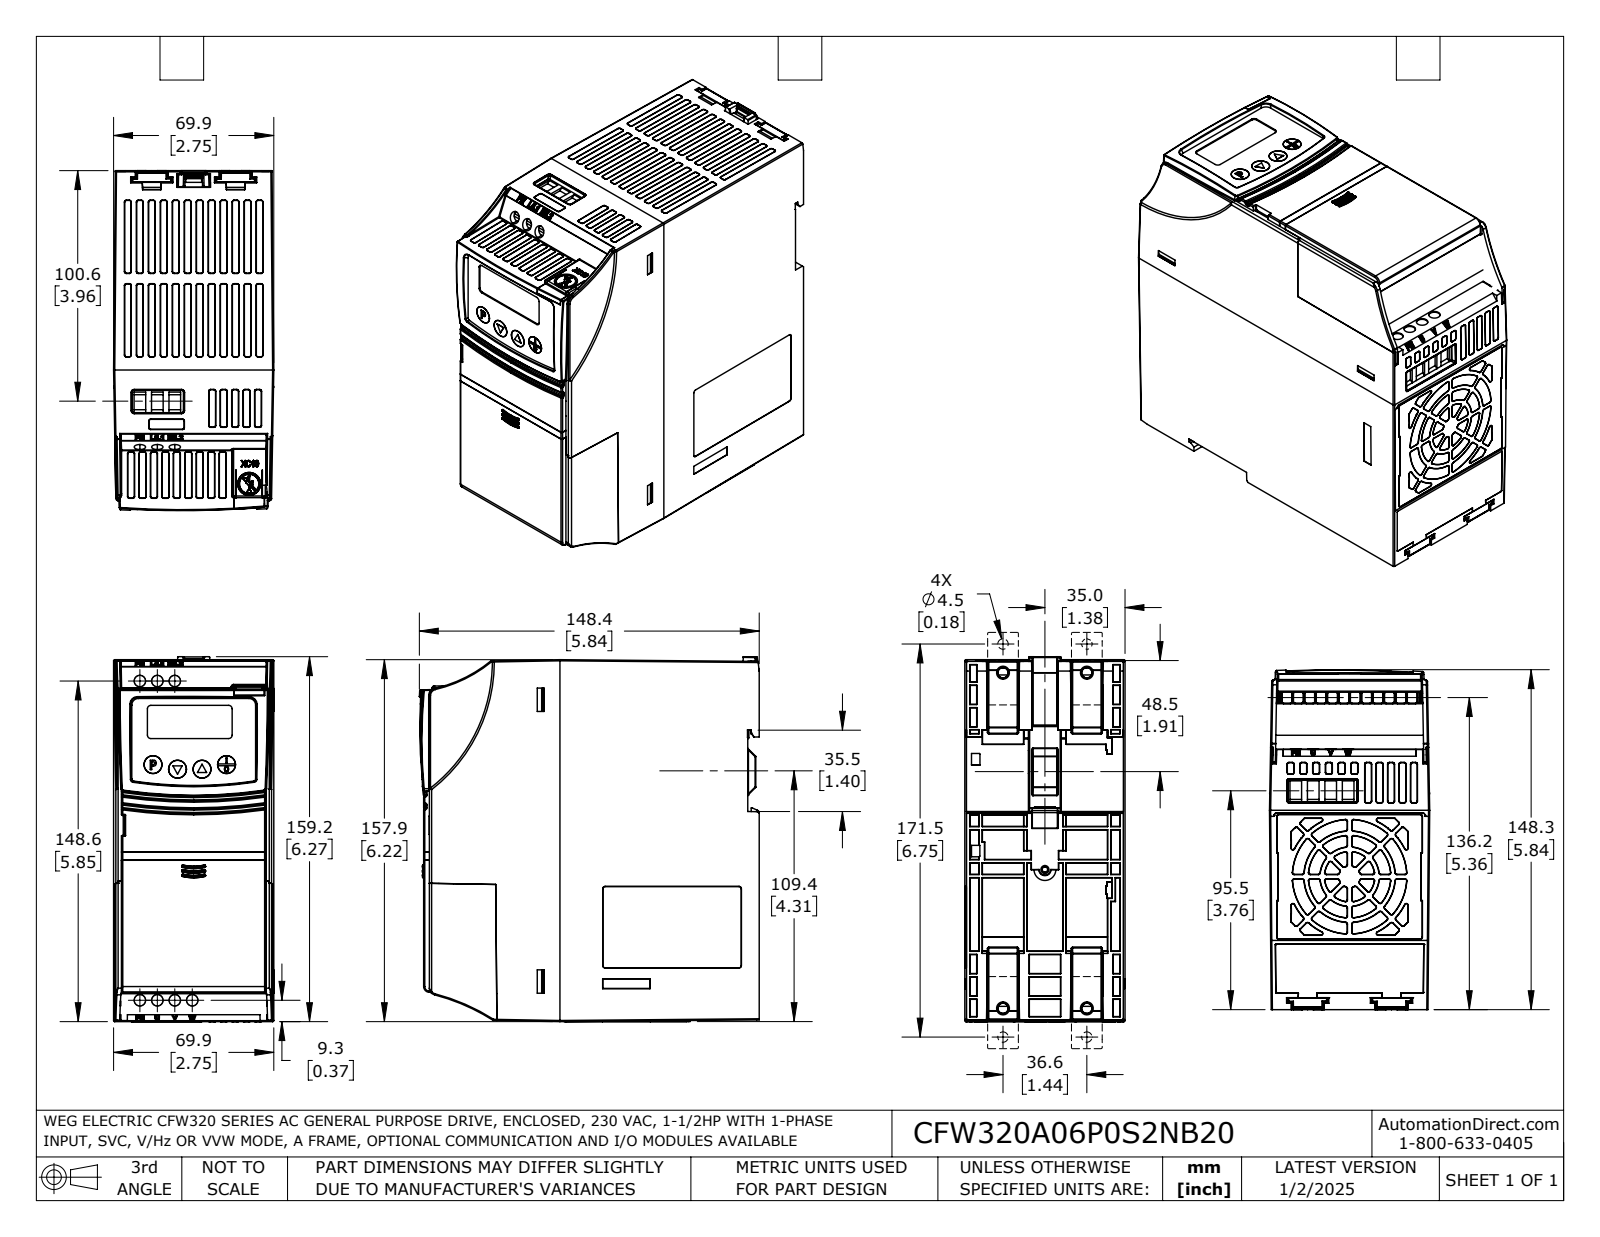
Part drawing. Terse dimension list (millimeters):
name: CFW320A06P0S2NB20
written by: SolidWorks 2021 (AUTOMOTIVE_DESIGN)
unit: mm
bodies: 6 solids, 3715 faces (1587 planar, 853 cylindrical, 1275 other)
size: 159.2 × 148.4 × 70
volume: 249 700 mm³; area: 199 400 mm²
holes: 3× ⌀5
rounds: 327× R0.3, 150× R0.5, 13× R1, 5× R0.8, 3× R3, 2× R0.3, 1× R2.5, 1× R3.2
face distances: 1.8, 1.4, 0.5, 1.3, 152.4, 135.4, 134, 141.5, 140.1, 6.1
hole spacings: 7.6, 15.2
